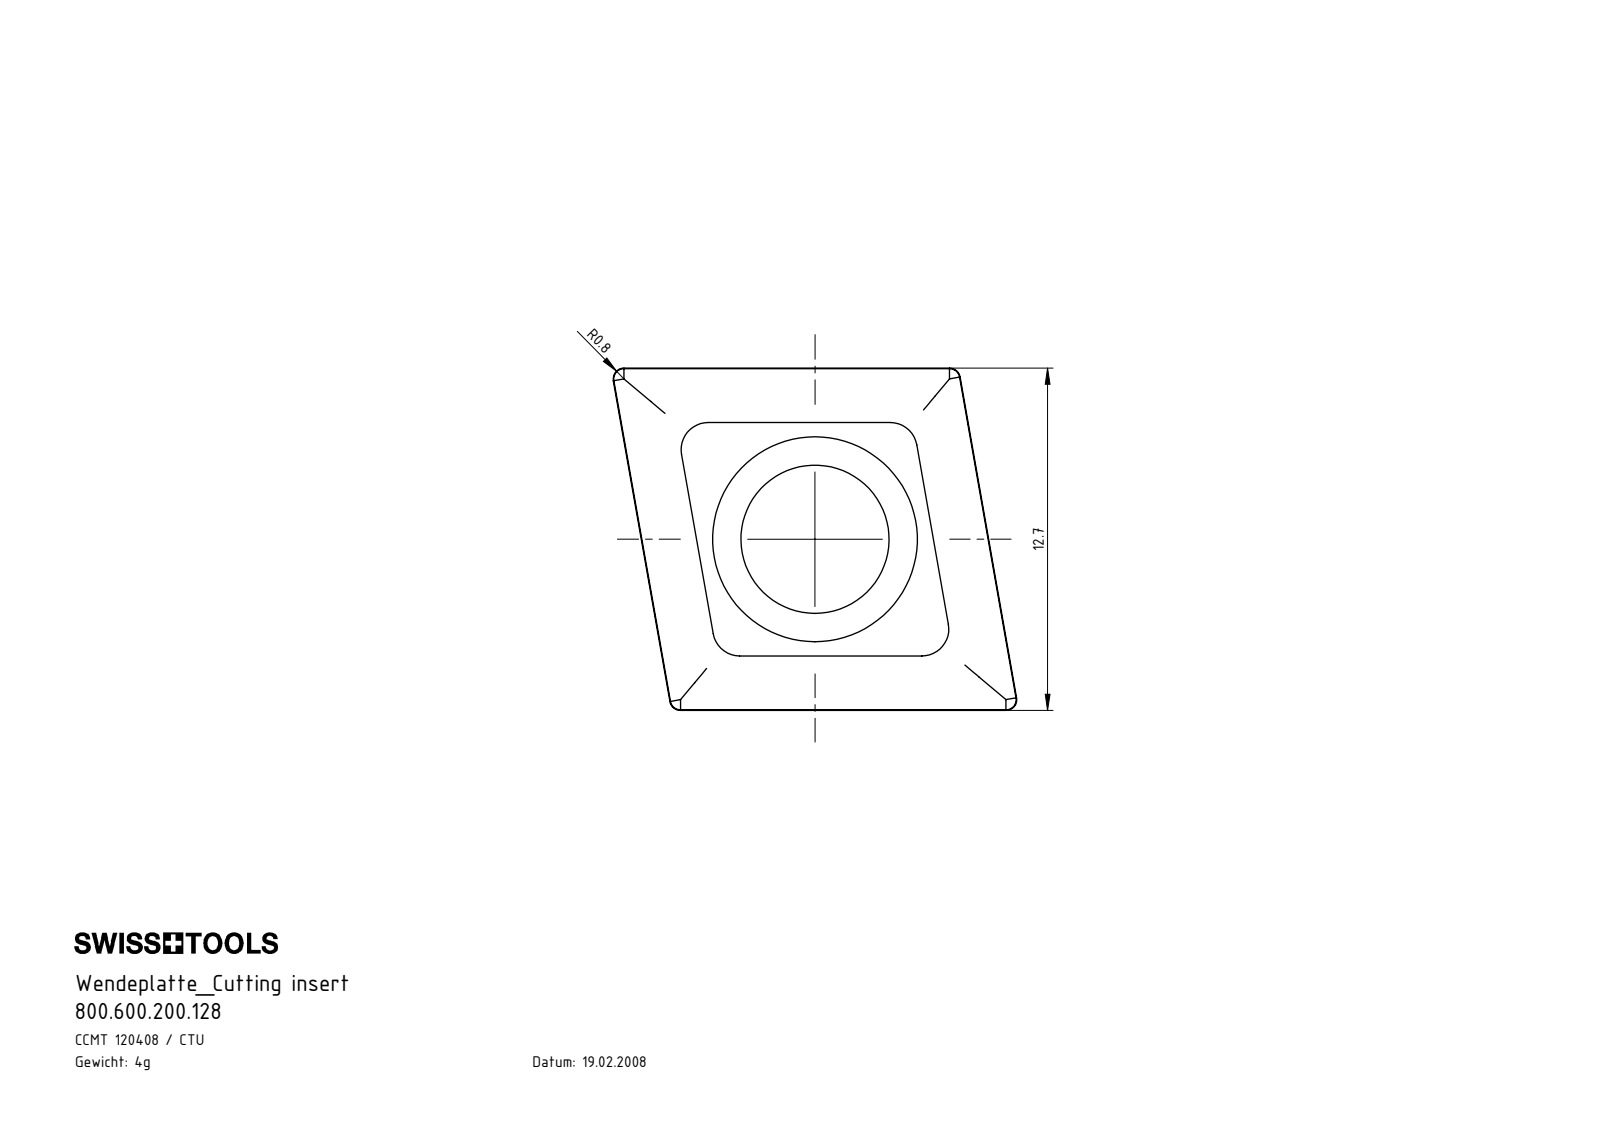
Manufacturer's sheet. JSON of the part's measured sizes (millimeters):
{"part_name": "800.600.200.128", "step_written_by": "SolidWorks 2022 (CONFIG_CONTROL_DESIGN)", "units": "millimeters", "bodies": {"solids": 1, "faces": 47, "planar": 15, "cylindrical": 4, "other": 28}, "overall_size": [14.83, 12.7, 4.76], "volume_mm3": 535, "surface_area_mm2": 574, "round_holes": [[5.5, 1], [7.6, 1]], "face_to_face_distances": [4.76, 5.33, 5.32]}
